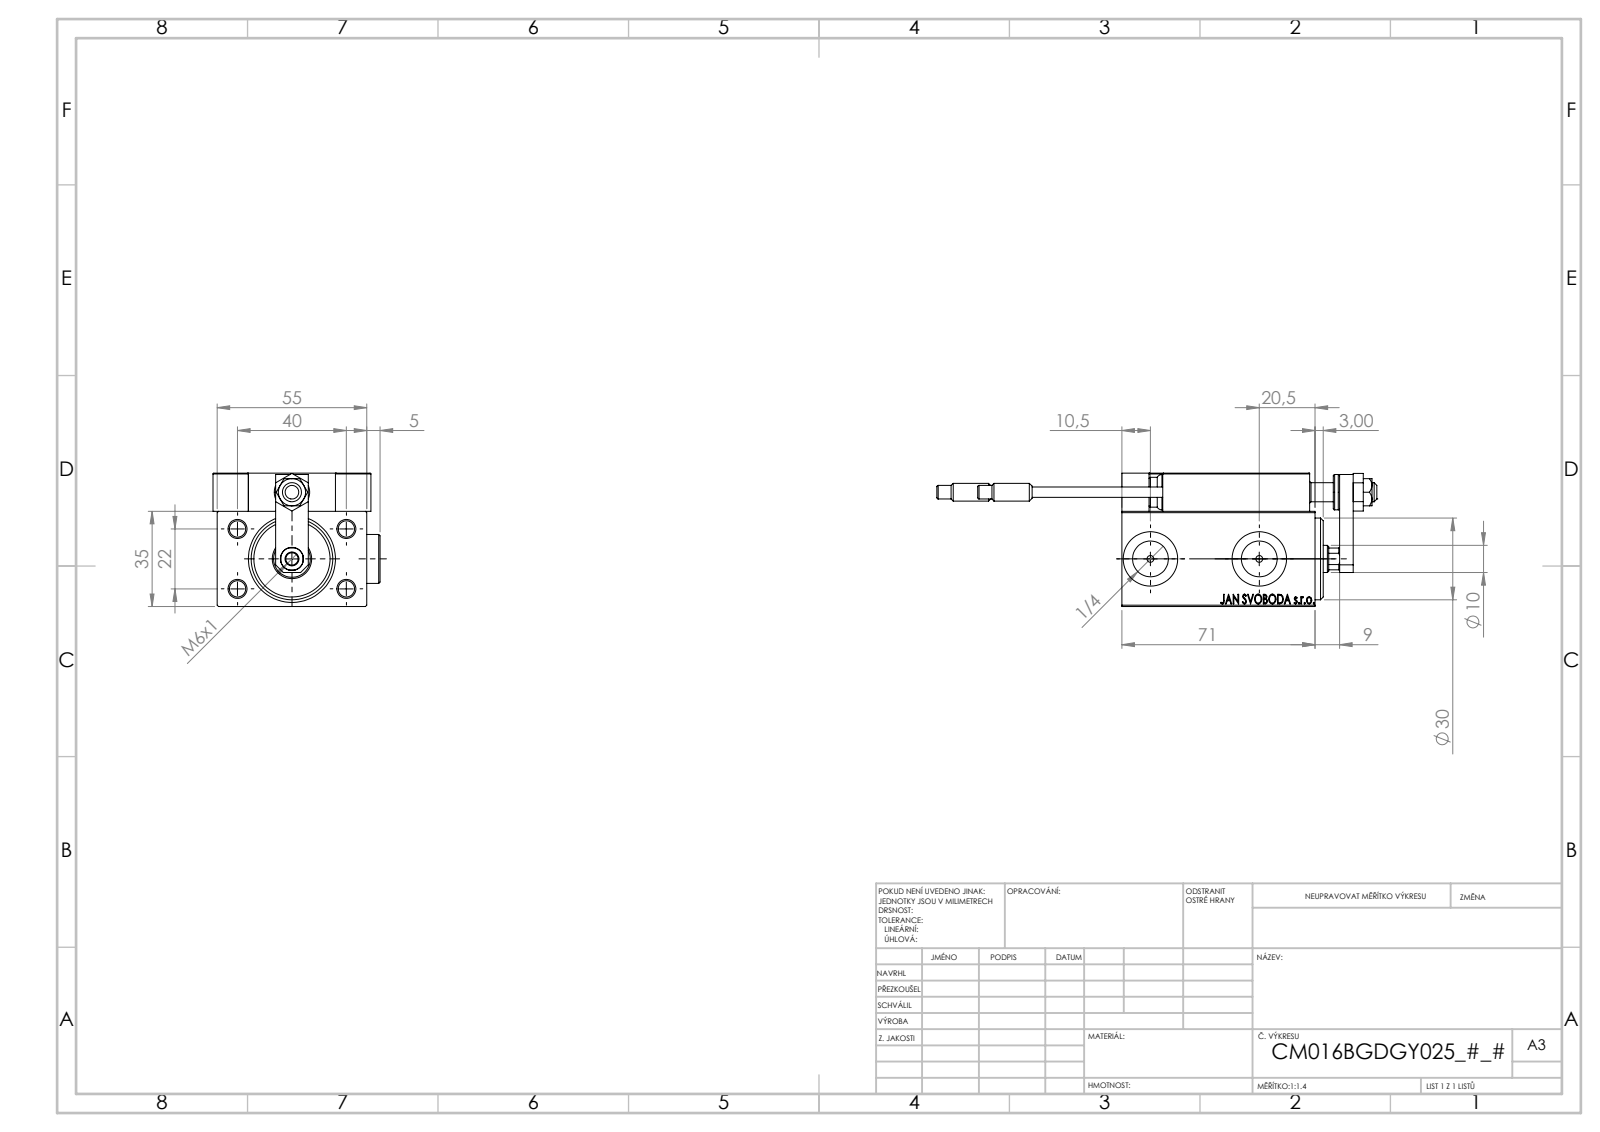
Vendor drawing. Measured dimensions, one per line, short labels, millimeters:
name: V450CM_B_Body; Block; Zatka_OIL_PORT; ZARAZKA (+8 more)
written by: SolidWorks 2019 (CONFIG_CONTROL_DESIGN)
unit: mm
bodies: 26 solids, 1394 faces (597 planar, 208 cylindrical, 589 other)
size: 161.7 × 61.4 × 49
volume: 171 724 mm³; area: 54 546 mm²
holes: 5× ⌀8, 4× ⌀3.2, 4× ⌀4, 4× ⌀6, 2× ⌀2.5, 2× ⌀5, 2× ⌀13.16, 2× ⌀20, 1× ⌀4.5, 1× ⌀7, 1× ⌀8.5, 1× ⌀10
bosses: 4× ⌀5, 2× ⌀18, 2× ⌀6.5, 2× ⌀3.8, 1× ⌀13, 1× ⌀11
rounds: 30× R0.3, 2× R3, 1× R4.5
face distances: 35, 5, 14, 49, 10, 3, 1.5, 55, 7, 13
hole spacings: 22.83, 40, 11.37, 20, 22, 23.09, 24.13, 29.59
